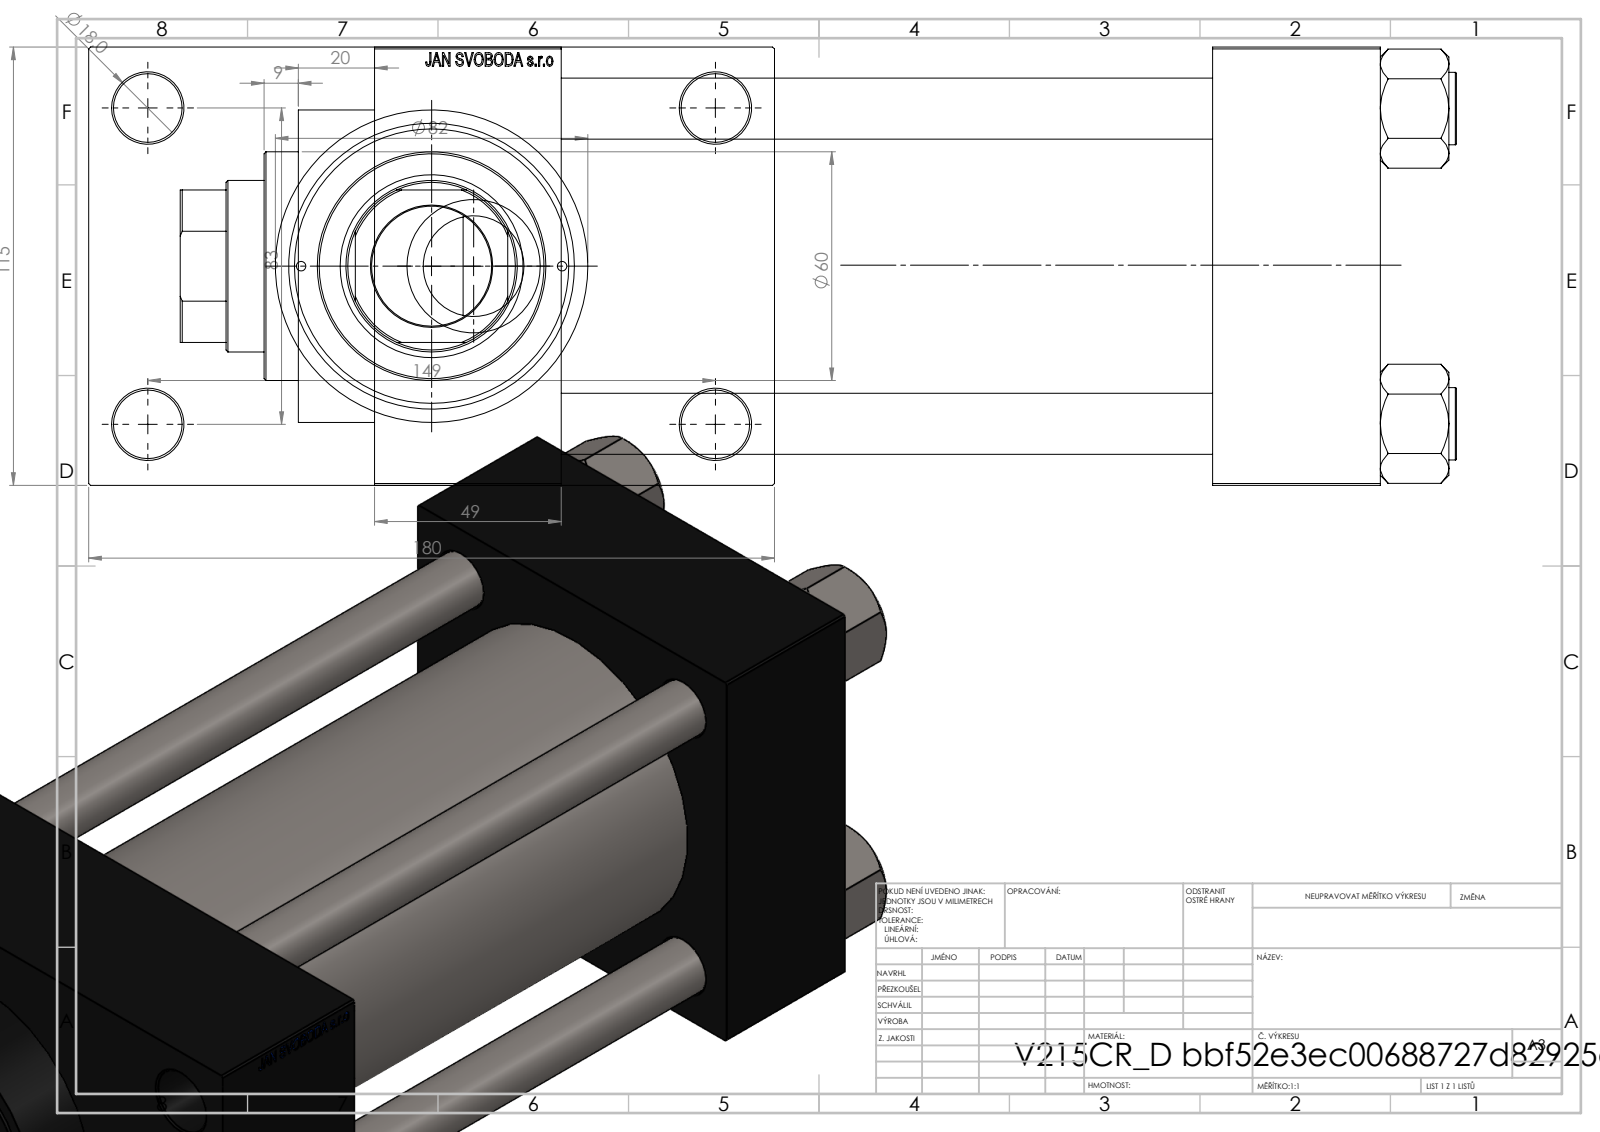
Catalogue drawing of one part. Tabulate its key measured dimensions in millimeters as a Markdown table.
| quantity | value |
| --- | --- |
| part name | V215CR_VCP_D; NUT_M5_D; V215CR_D_Body; V215CR_D_TYCINKA (+1 more) |
| STEP written by | SolidWorks 2019 (CONFIG_CONTROL_DESIGN) |
| units | millimeters |
| bodies | 11 solids, 1159 faces (547 planar, 92 cylindrical, 520 other) |
| overall size | 335 × 180 × 115 |
| volume | 2 337 000 mm³ |
| surface area | 393 045 mm² |
| round holes (diameter × count) | 16 × 4, 18 × 4, 2.5 × 2, 7 × 2, 26.44 × 2, 35 × 2, 31.5 × 1, 45 × 1, 48 × 1, 61 × 1, 72 × 1, 80 × 1 |
| round bosses / shafts (diameter × count) | 19 × 4, 86 × 1, 82 × 1, 60 × 1 |
| partial cylindrical surfaces (radius × count) | 22 × 1 |
| main face-to-face distances | 115, 171, 220, 49, 44, 215, 264, 147.5, 32.5, 180 |
| hole center spacings | 33.15, 41.96, 57.81, 58.48, 82.7, 85.28, 86.17, 89.24 |
